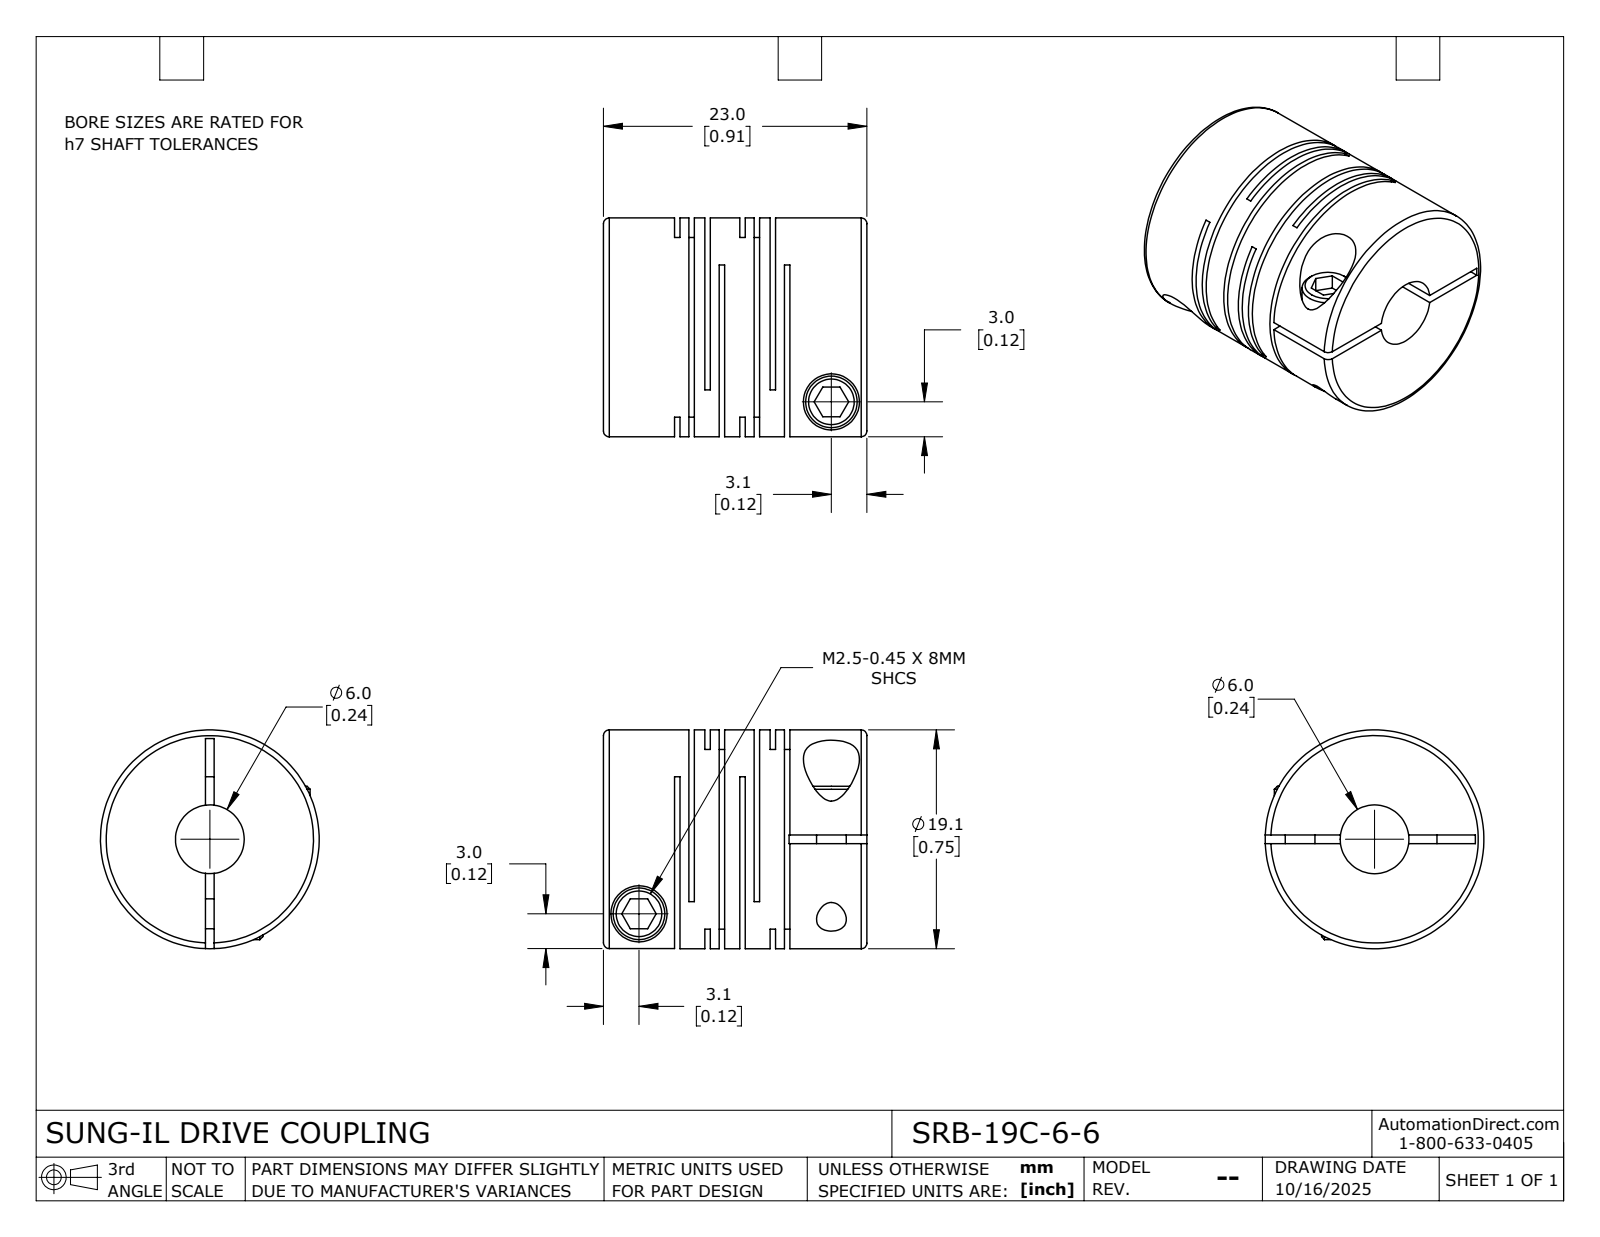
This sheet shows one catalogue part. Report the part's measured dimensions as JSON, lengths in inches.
{"part_name": "SRB-19C-6-6", "step_written_by": "SolidWorks 2024 (CONFIG_CONTROL_DESIGN)", "units": "inches", "bodies": {"solids": 1, "faces": 115, "planar": 60, "cylindrical": 42, "other": 13}, "overall_size": [0.906, 0.752, 0.752], "volume_in3": 0.298, "surface_area_in2": 9.322, "round_holes": [[0.102, 2], [0.193, 2], [0.236, 1]], "round_bosses_or_shafts": [[0.177, 2], [0.752, 1]], "face_to_face_distances": [0.104, 0.224, 0.019, 0.049, 0.085, 0.12, 0.206, 0.03, 0.175, 0.055]}
